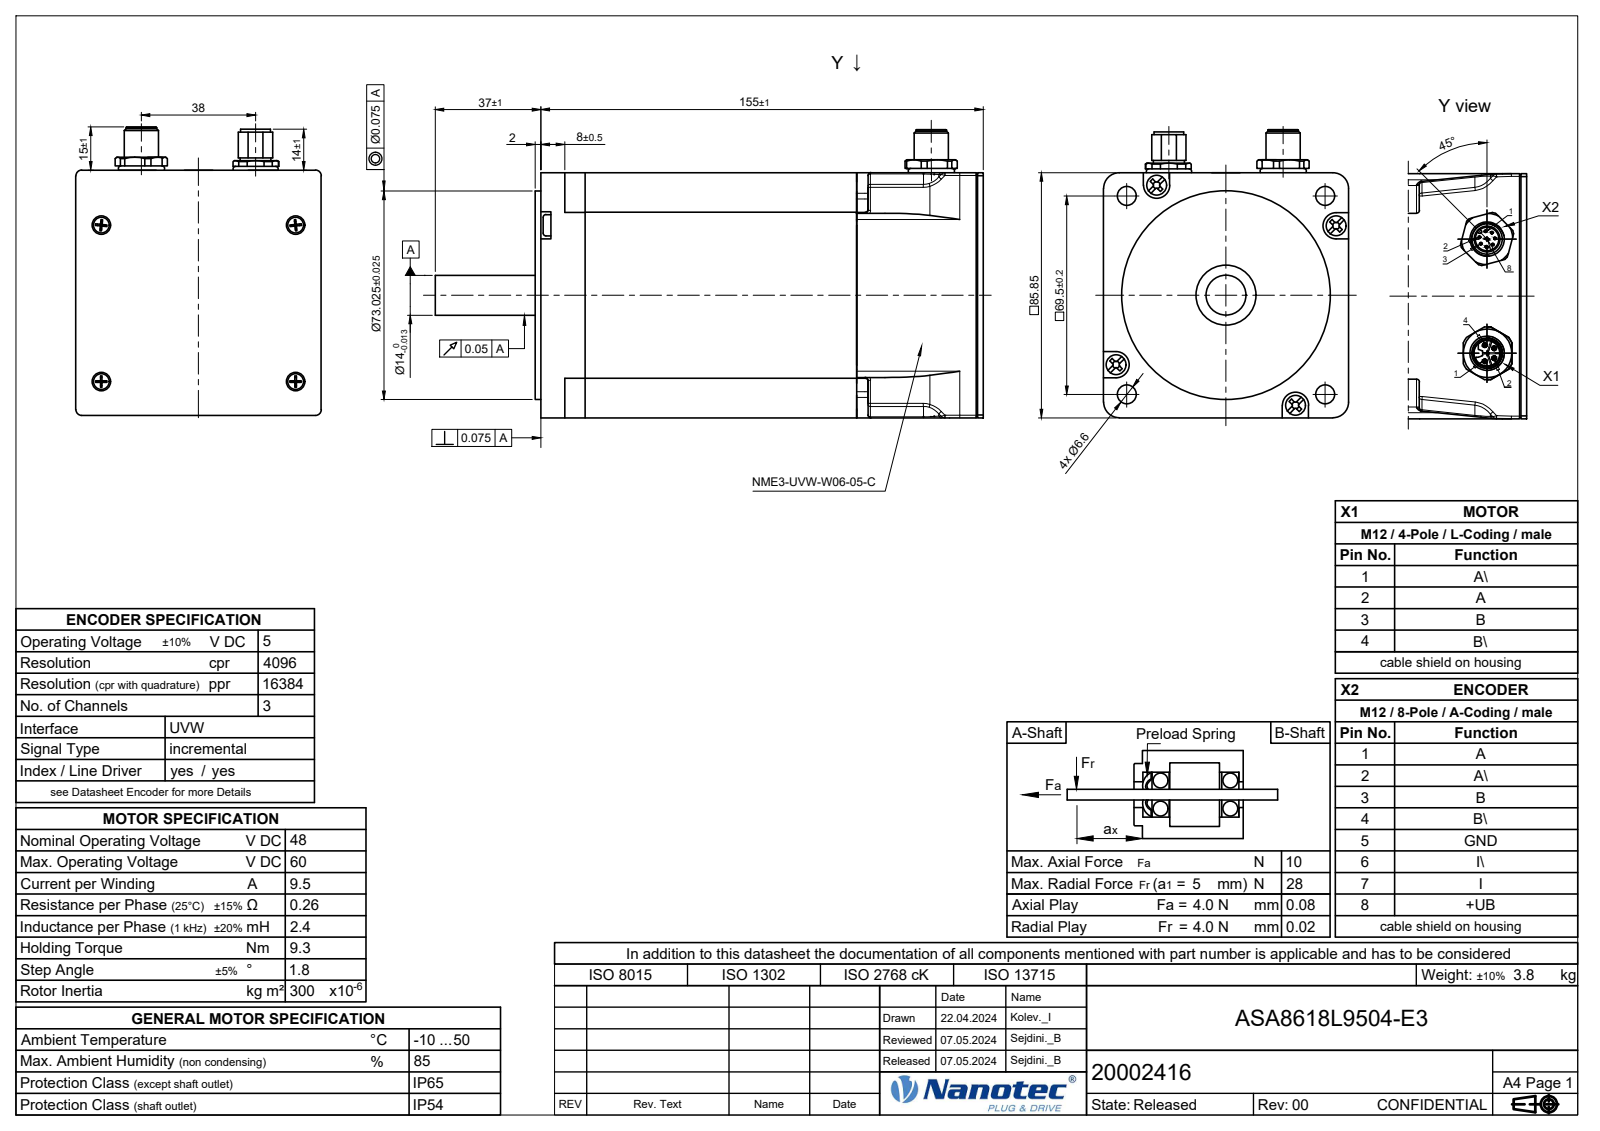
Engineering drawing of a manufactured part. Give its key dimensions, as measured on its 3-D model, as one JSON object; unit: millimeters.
{"part_name": "D-00005796", "step_written_by": "Autodesk Inventor 2021 (AUTOMOTIVE_DESIGN)", "units": "millimeters", "bodies": {"solids": 1, "faces": 663, "planar": 252, "cylindrical": 171, "other": 240}, "overall_size": [192.08, 100.5, 85.9], "volume_mm3": 1068000, "surface_area_mm2": 73659, "round_holes": [[1.55, 5], [2.46, 4], [3.24, 4], [3.4, 4], [6.6, 4], [1.5, 1], [1.6, 1], [2.25, 1], [8.3, 1], [8.9, 1], [9.2, 1], [10.1, 1]], "round_bosses_or_shafts": [[1, 8], [2.8, 4], [1.5, 4], [73.03, 1], [14, 1], [13, 1], [12, 1], [10.8, 1]], "partial_cylinders_radius": [[2, 20], [4.6, 20], [1, 16], [0.3, 10], [5.9, 8], [0.2, 6], [5.5, 4], [18, 4]], "face_to_face_distances": [85.85, 85.9, 157, 2, 155, 58.1, 71.97, 13.88, 13.87, 71.98], "hole_center_spacings": [2.94, 3.46, 5.59, 64.42, 69.5, 13.46, 52.83, 55.9]}
